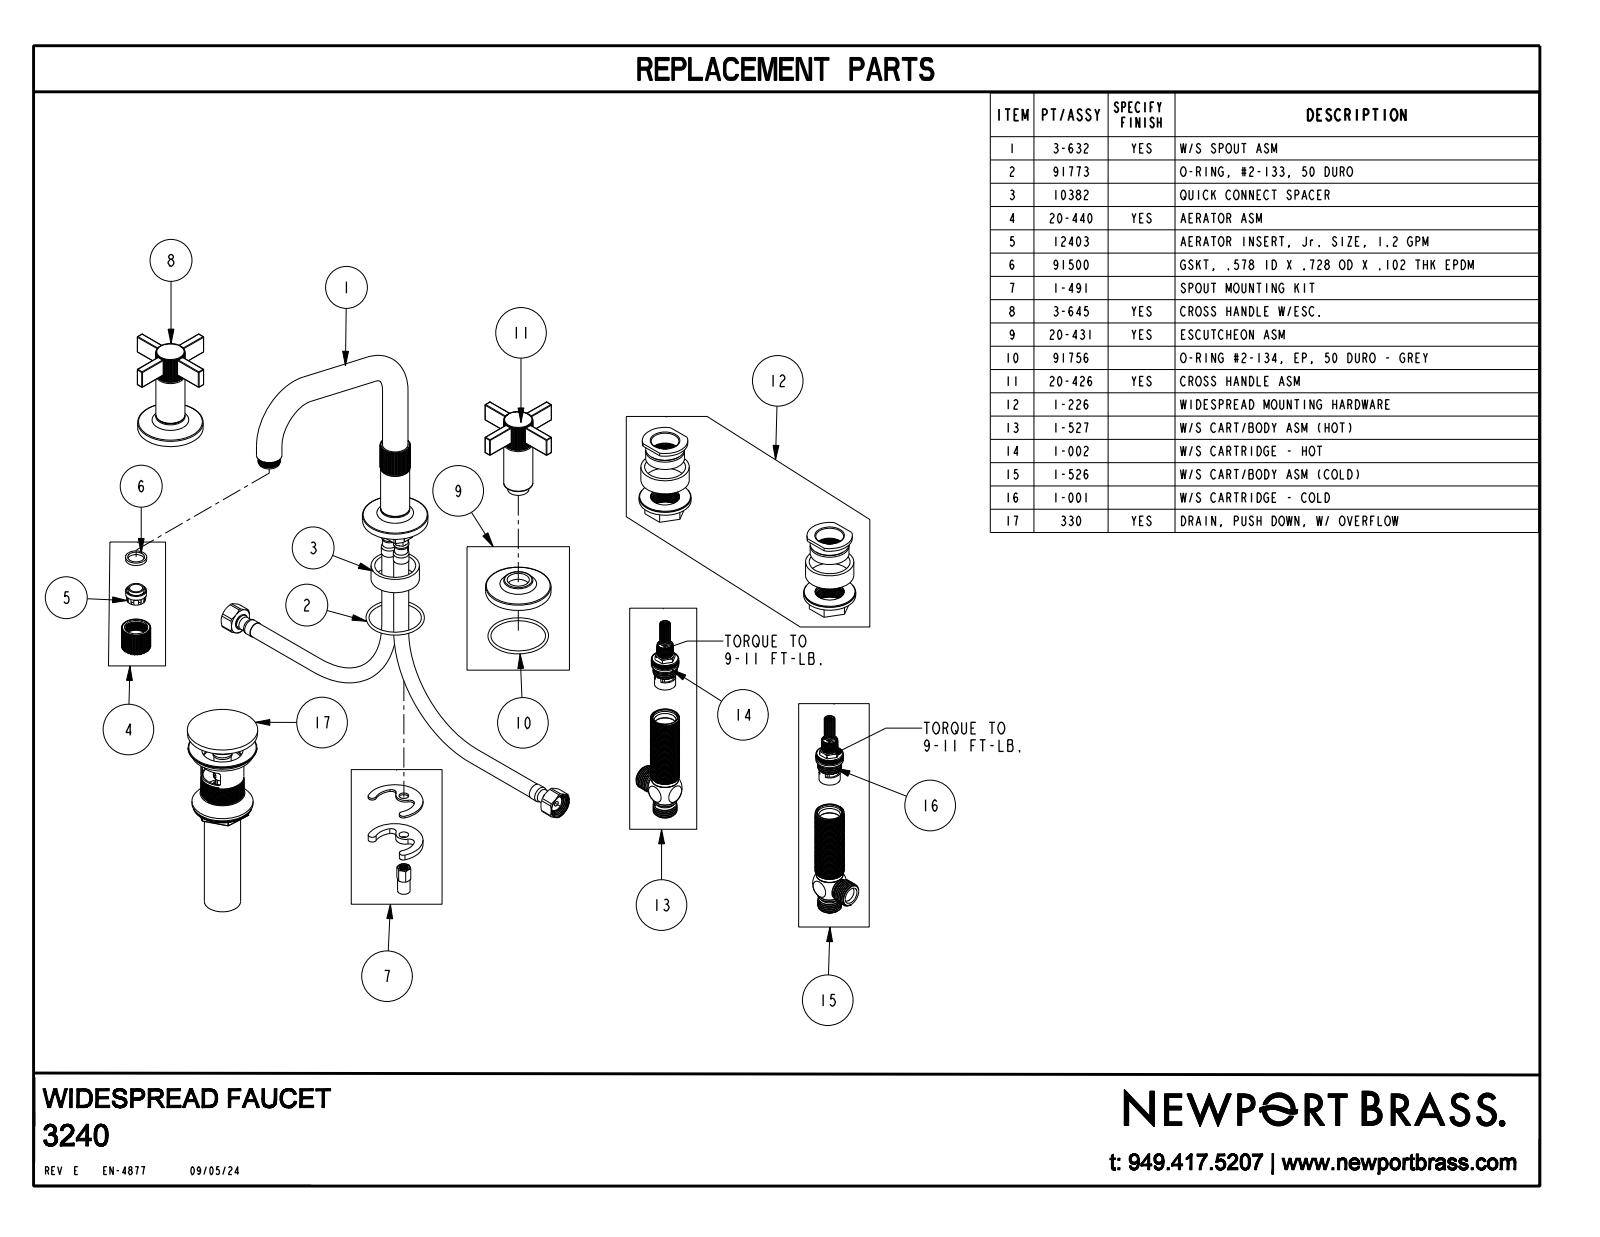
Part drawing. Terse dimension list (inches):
name: 3240
written by: CREO PARAMETRIC BY PTC INC, 2018400 (CONFIG_CONTROL_DESIGN)
unit: in
bodies: 3 solids, 1334 faces (692 planar, 494 cylindrical, 148 other)
size: 11 × 8.147 × 8.125
volume: 18.61 in³; area: 112.3 in²
holes: 1× ⌀0.881
bosses: 3× ⌀2.25, 3× ⌀1, 2× ⌀0.875, 2× ⌀0.85, 2× ⌀0.52, 1× ⌀0.97, 1× ⌀0.875
rounds: 68× R0.02, 12× R0.03, 1× R0.5, 1× R0.52
face distances: 8, 0.25, 0.25, 2.496, 3.146, 0.65, 0.624, 3.201, 0.705, 0.055
